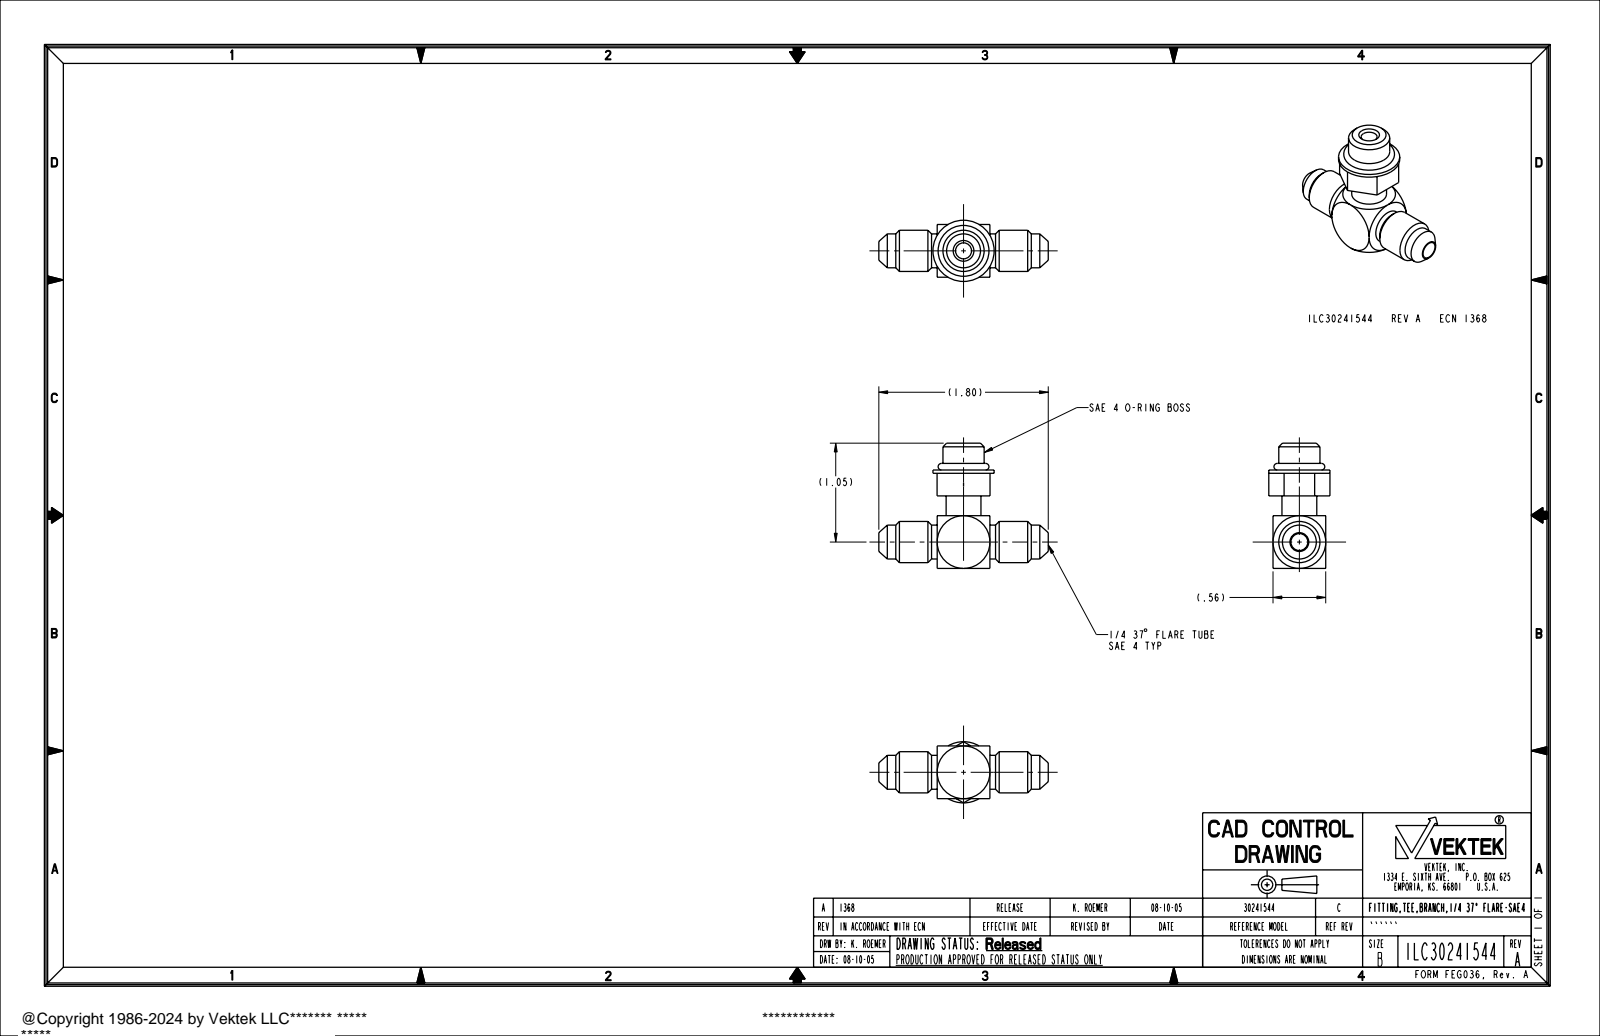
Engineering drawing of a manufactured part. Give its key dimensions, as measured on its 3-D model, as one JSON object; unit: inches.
{"part_name": "ILC30241544", "step_written_by": "PRO/ENGINEER BY PARAMETRIC TECHNOLOGY CORPORATION, 2004290 (AUTOMOTIVE_DESIGN_CC2)", "units": "inches", "bodies": {"solids": 1, "faces": 74, "planar": 20, "cylindrical": 28, "other": 26}, "overall_size": [1.8, 1.33, 0.65], "volume_in3": 0.405, "surface_area_in2": 6.413, "round_holes": [[0.17, 1], [0.18, 1]], "round_bosses_or_shafts": [[0.437, 2], [0.65, 1], [0.37, 1], [0.36, 1]], "face_to_face_distances": [0.56, 0.562, 0.77, 1.045, 0.275, 0.561, 0.21, 0.485, 1.33, 0.285]}
